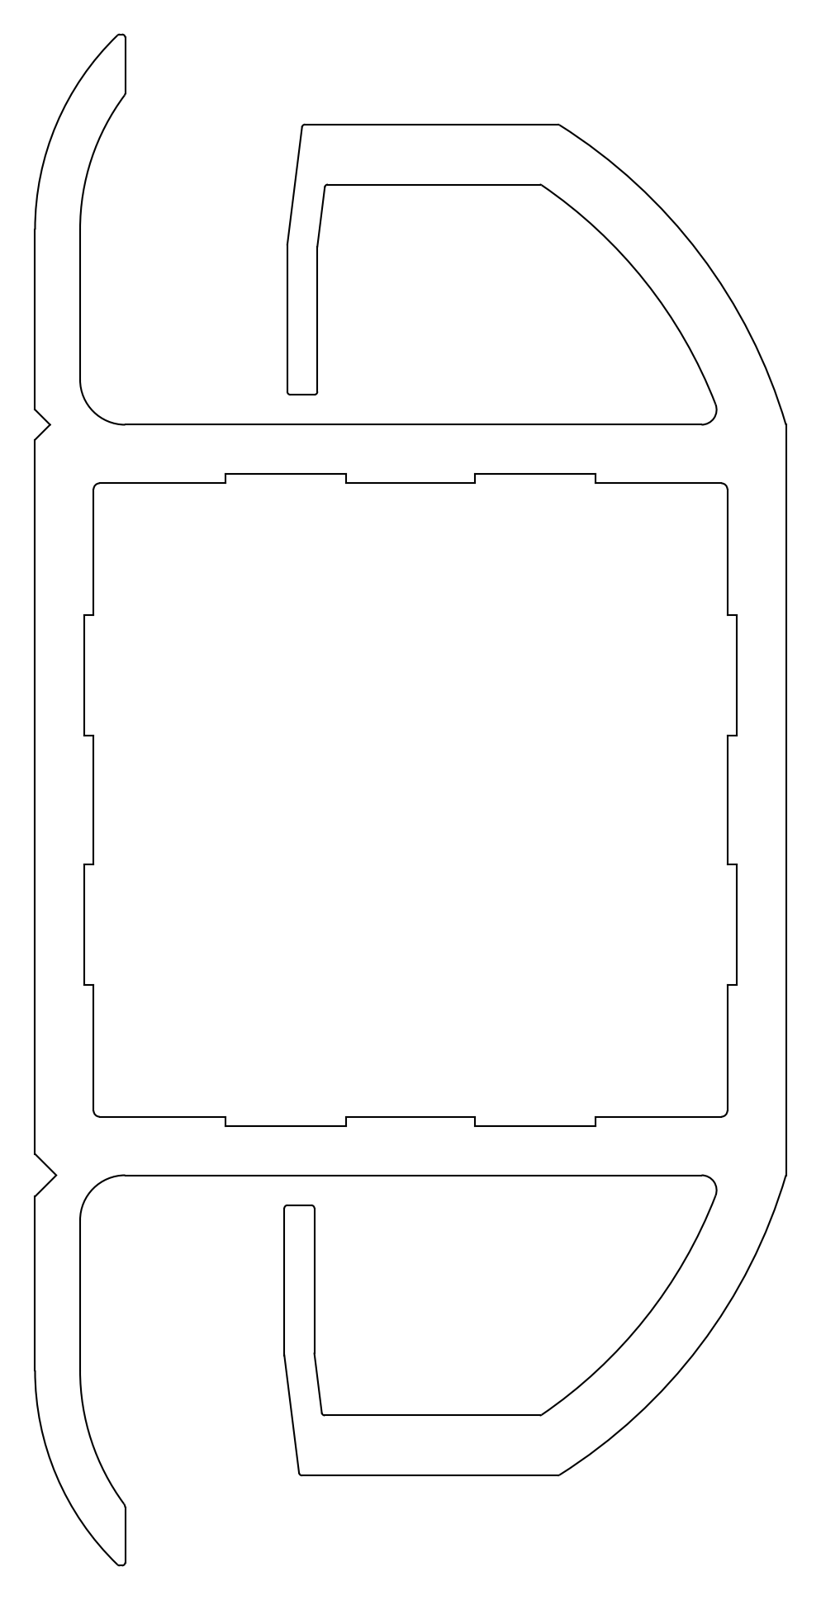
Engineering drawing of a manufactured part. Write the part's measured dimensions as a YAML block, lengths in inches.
step_written_by: "THINKDESIGN (CONFIG_CONTROL_DESIGN)"
units: inches
bodies: {solids: 1, faces: 102, planar: 68, cylindrical: 34, other: 0}
overall_size: [3.937, 2.008, 0.984]
volume: 1.846
surface_area: 54.64
partial_cylinders:
  - {radius: 0.004, count: 17}
  - {radius: 0.008, count: 5}
  - {radius: 0.02, count: 2}
  - {radius: 0.059, count: 2}
  - {radius: 0.295, count: 2}
  - {radius: 0.354, count: 2}
  - {radius: 0.619, count: 2}
  - {radius: 0.698, count: 2}
face_to_face_distances: [0.077, 0.907, 0.984, 0.919, 0.065, 0.843, 0.831, 0.394, 0.47, 1.301]
